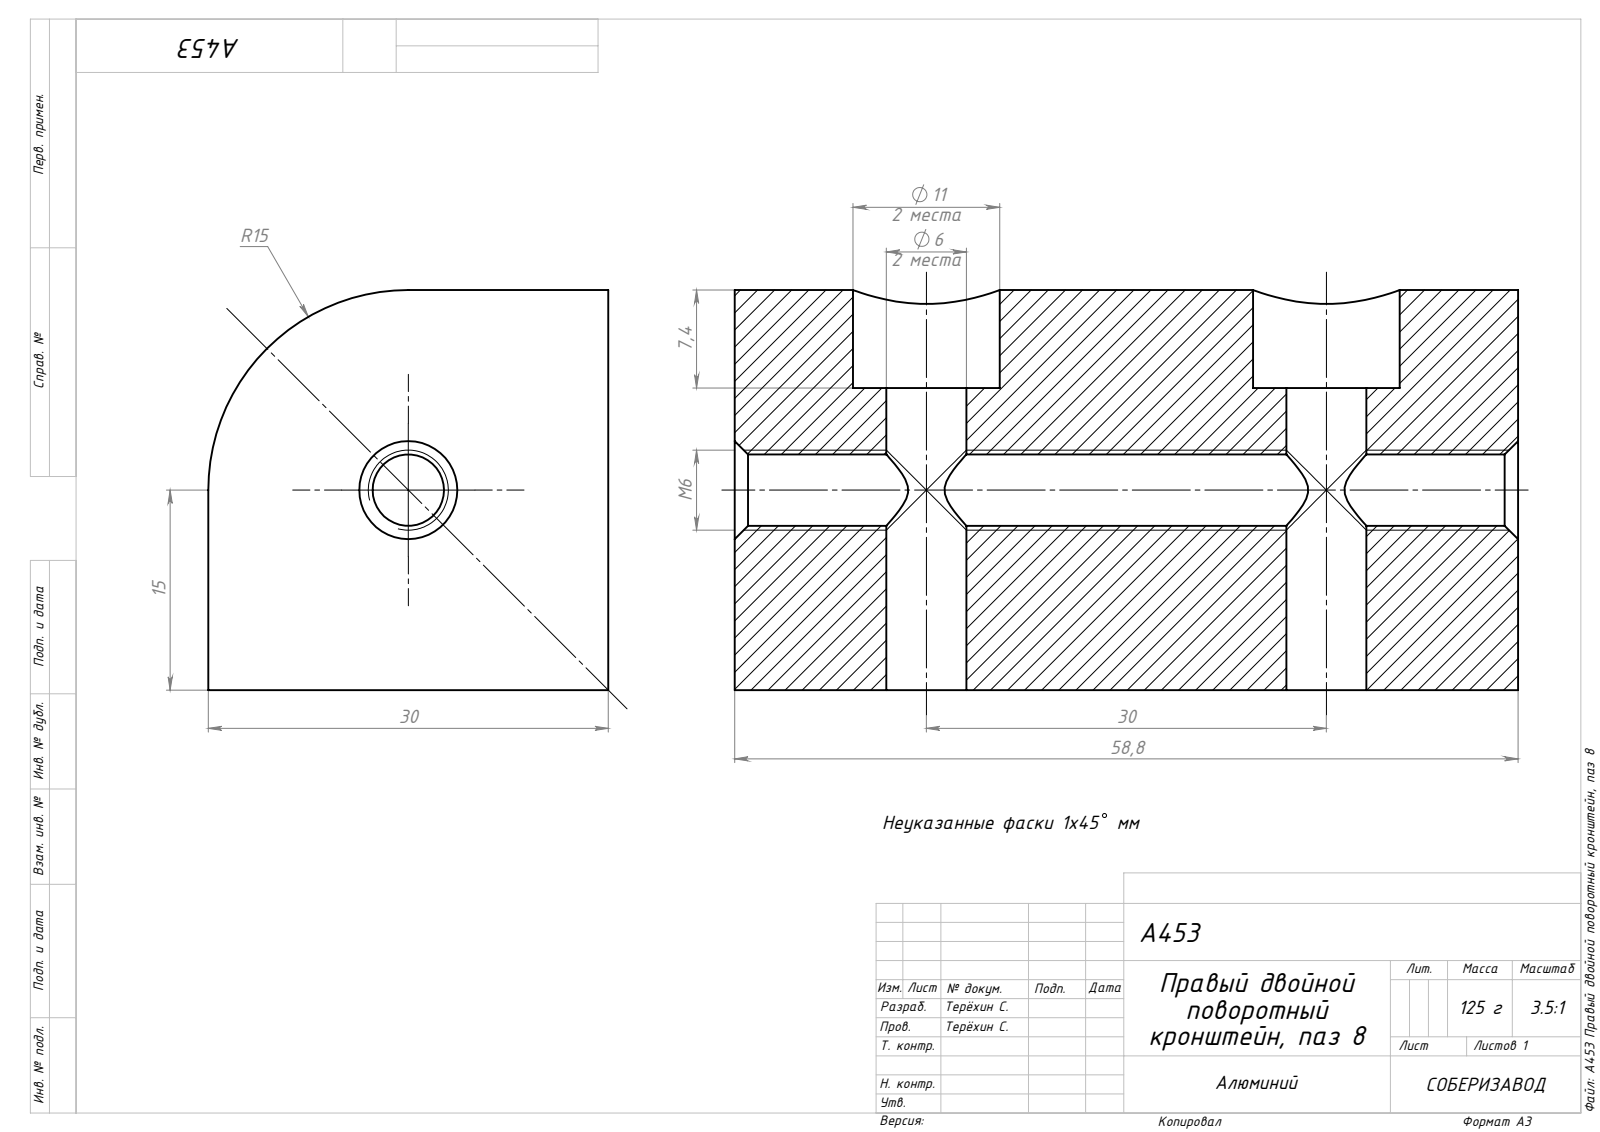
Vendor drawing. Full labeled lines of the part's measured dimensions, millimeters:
Part name (STEP PRODUCT): A453 Правый двойной поворотный кронштейн, паз 8
STEP written by: SolidWorks 2021 (AUTOMOTIVE_DESIGN)
Units: millimetres
Bodies: 1 solid, 27 faces (8 planar, 15 cylindrical, 4 other)
Overall size (bounding box): 58.75 × 30 × 30
Volume: 46 284 mm³ · Surface area: 10 274 mm²
Round holes (diameter × count): ⌀6 ×2, ⌀11 ×2, ⌀5.35 ×1
Partial cylindrical surfaces — rounded edges, fillets, slot ends (radius × count): R15 ×1
Main face-to-face distances: 30, 58.75, 22.65, 7.35
Hole centre spacings: 30.01
